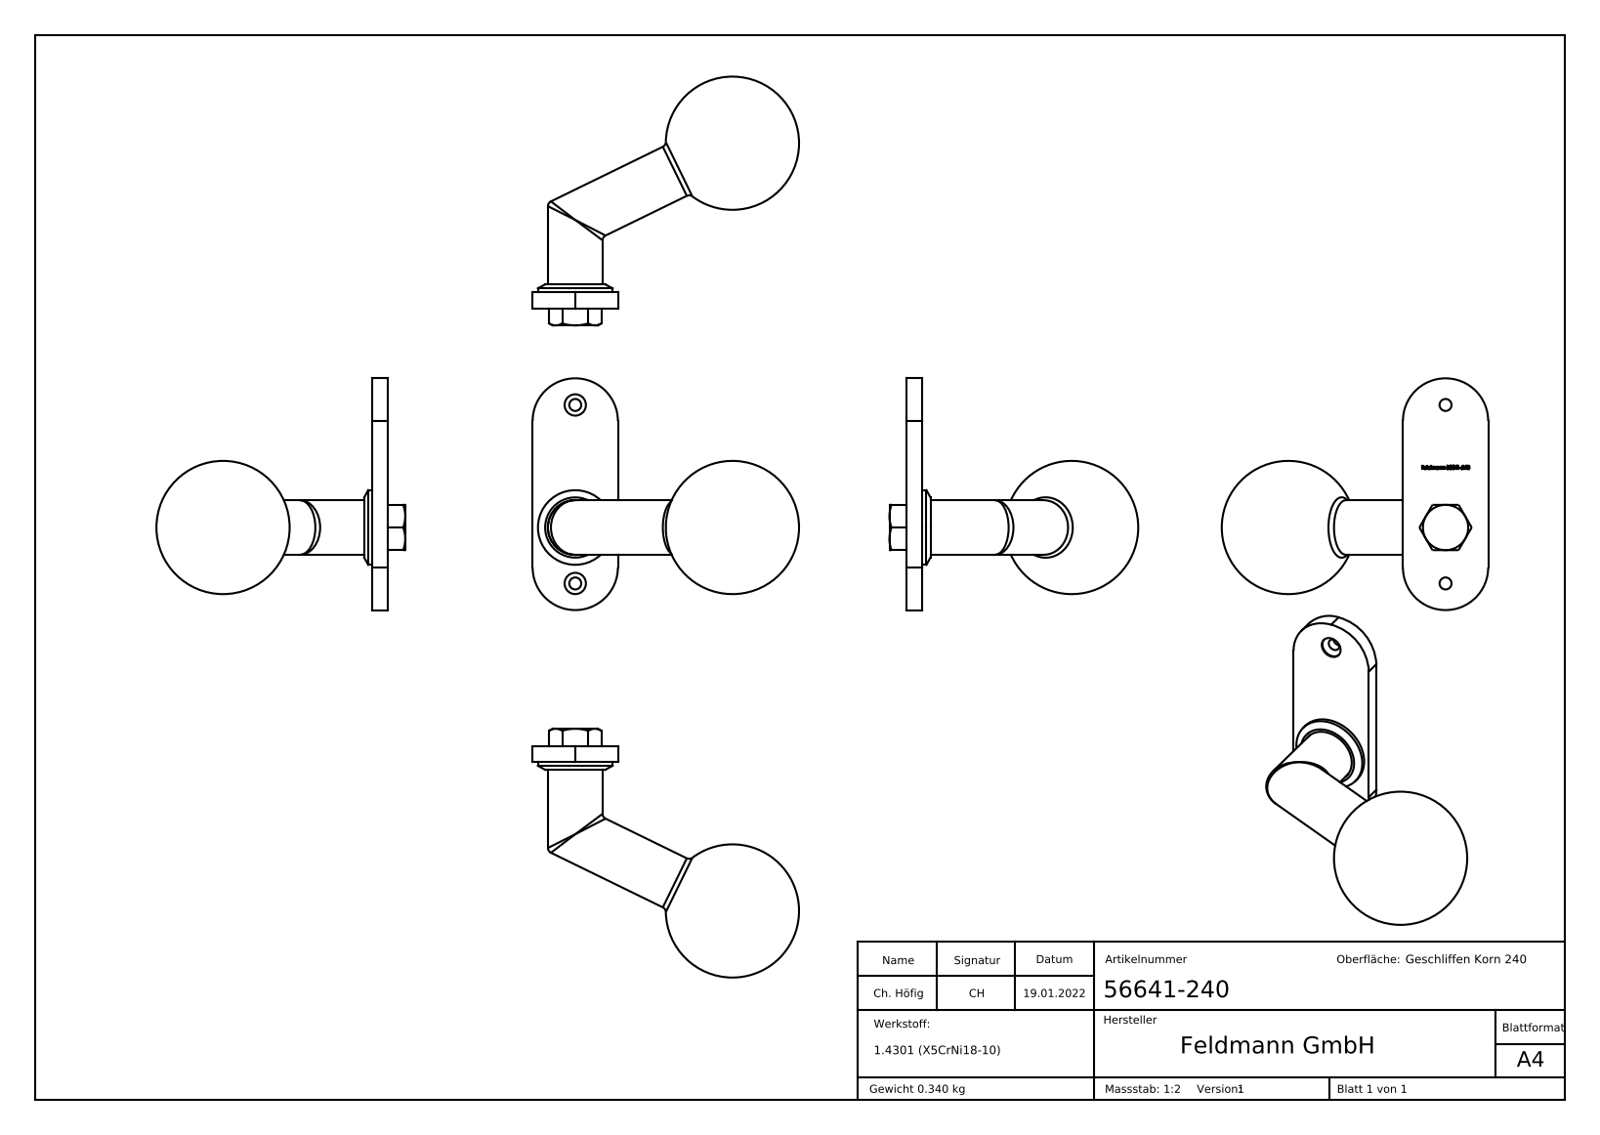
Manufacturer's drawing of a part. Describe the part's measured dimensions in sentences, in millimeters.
The part is named "5664x-240 Teil1_56641-240 Teil1; 5664x-240 Teil1; 56641-240; DIN 931 (+5 more)". Its 3-D file was written by "SolidWorks 2018 (CONFIG_CONTROL_DESIGN)". It is 5 solids with 350 faces: 182 planar, 49 cylindrical and 119 other. Overall it measures 100 by 93.4 by 87 millimeters. Its volume is 43 091 cubic millimeters and its surface area 33 425 square millimeters. Round holes: 2 of diameter 4.5, 2 of diameter 8, 2 of diameter 16.5, 1 of diameter 16.4, 1 of diameter 20.6. Round bosses or shafts: 2 of diameter 20.5, 1 of diameter 28, 1 of diameter 18, 1 of diameter 15, 1 of diameter 10, 1 of diameter 7.7. Partial cylindrical surfaces (rounded edges, fillets, slot ends): 2 of radius 16, 1 of radius 4.25. The main face-to-face distances are 6, 32, 1.2, 7.2, 12.25, 6.4, 12.4, 13.6, 17, 28.6. The hole center spacings are 21, 46, 67.
